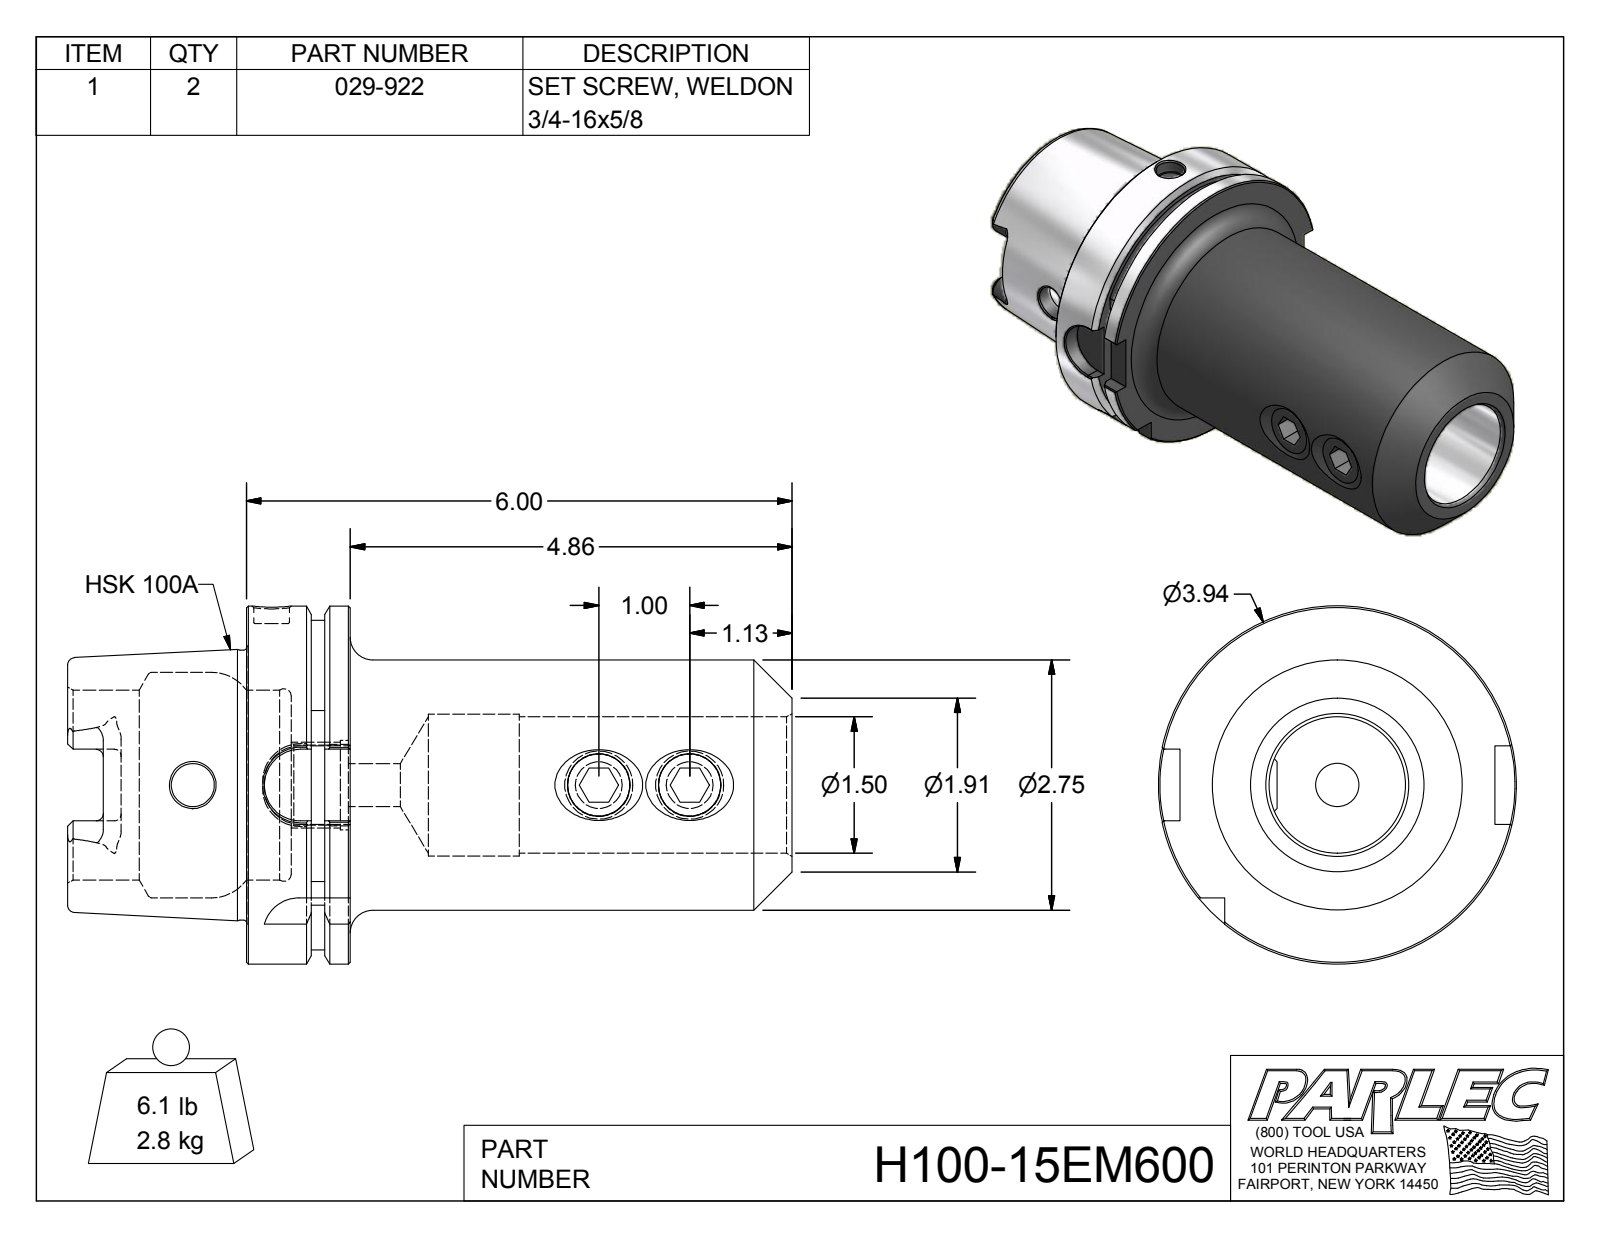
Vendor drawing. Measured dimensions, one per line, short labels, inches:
name: H100-15EM600; 029-922
written by: Autodesk Inventor 2012 (AUTOMOTIVE_DESIGN)
unit: in
bodies: 3 solids, 154 faces (62 planar, 38 cylindrical, 54 other)
size: 7.969 × 3.937 × 3.937
volume: 36.16 in³; area: 142.6 in²
holes: 2× ⌀0.472, 2× ⌀0.682, 1× ⌀0.394, 1× ⌀0.881, 1× ⌀0.985, 1× ⌀1.5, 1× ⌀1.56, 1× ⌀2.087, 1× ⌀2.48
bosses: 2× ⌀0.75, 1× ⌀3.937, 1× ⌀2.967, 1× ⌀2.75
rounds: 6× R0.079, 4× R0.192, 4× R0.394, 1× R1.811
face distances: 1.142, 0.492, 0.65, 1.969, 2.461, 3.11, 7.969, 6, 5.508, 4.858
hole spacings: 1, 4.466, 5.466
